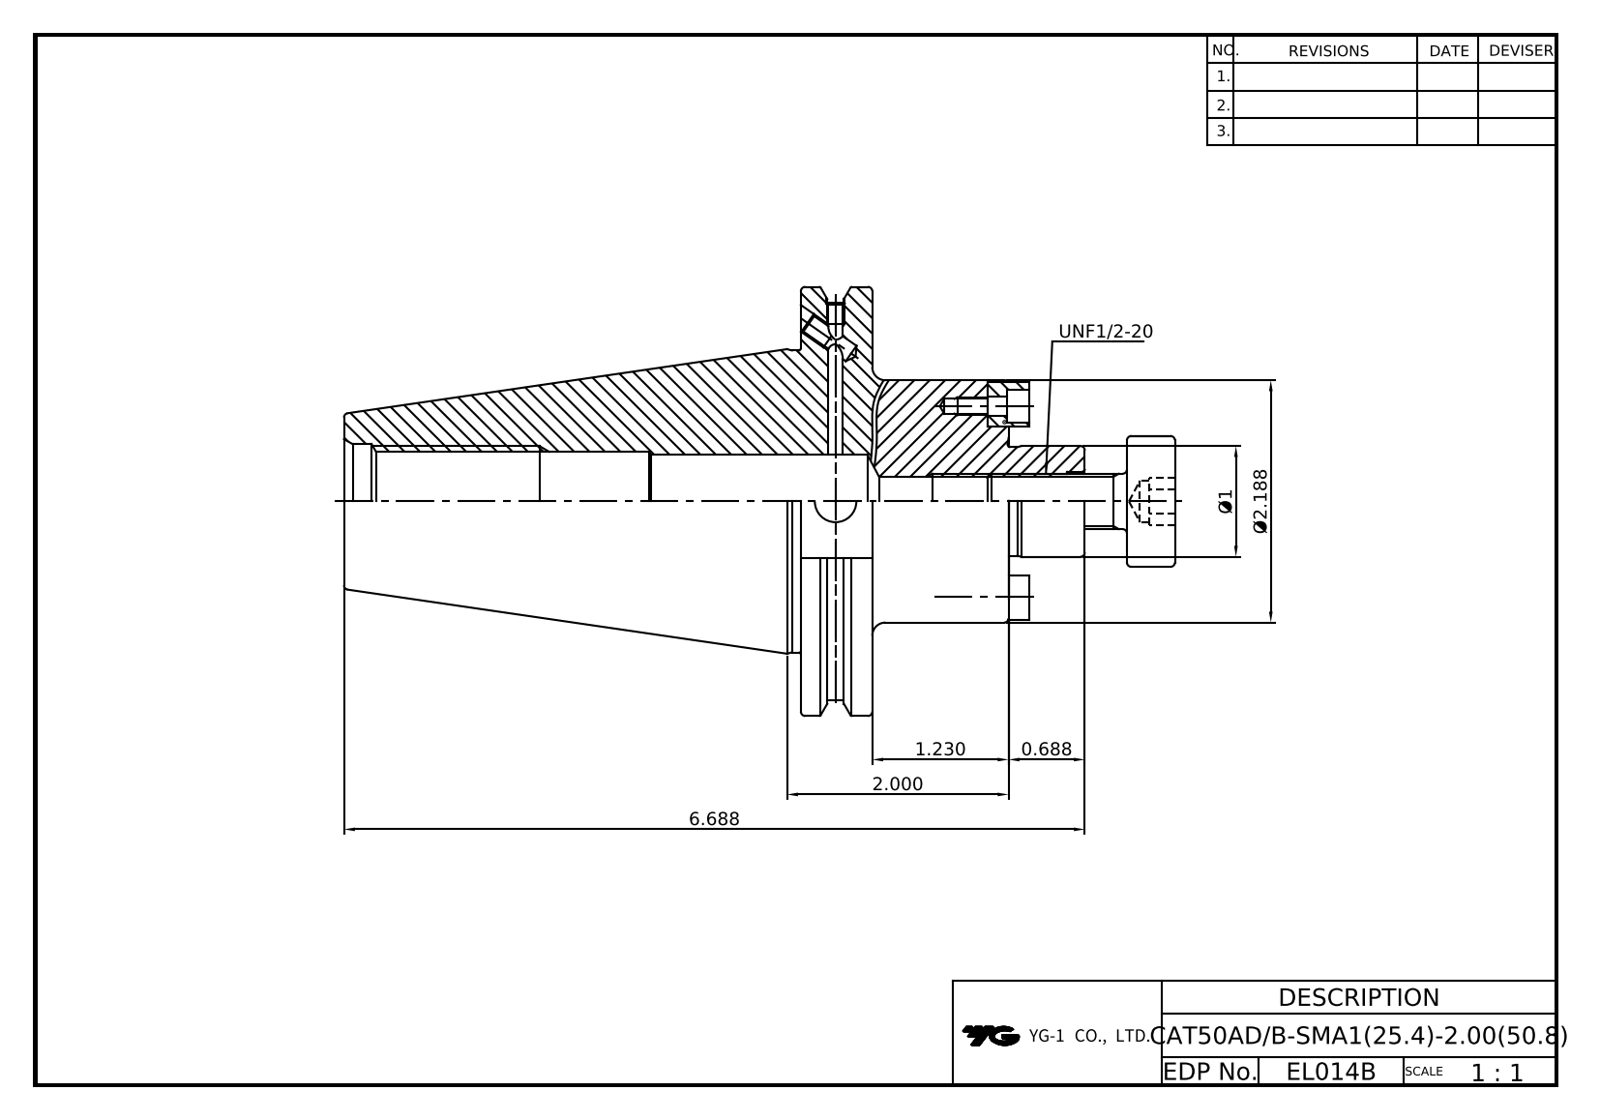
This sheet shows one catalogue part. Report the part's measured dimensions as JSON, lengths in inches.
{"part_name": "LO-CAT50ADB-SMA25.4-50.8; DRIVE KEY-9.52x9.52x10.2; HEX'' WRENCH BOLT-UNC#8-32x3_8L; COLLAR BOLT-UNF1_2-20x32L", "step_written_by": "Autodesk Inventor 2025 (AP242_MANAGED_MODEL_BASED_3D_ENGINEERING_MIM_LF)", "units": "inches", "bodies": {"solids": 6, "faces": 167, "planar": 88, "cylindrical": 43, "other": 36}, "overall_size": [7.515, 3.875, 3.728], "volume_in3": 25.36, "surface_area_in2": 92.3, "round_holes": [[0.128, 2], [0.13, 2], [0.163, 2], [0.165, 2], [0.177, 2], [0.197, 2], [0.295, 2], [0.375, 2], [0.446, 1], [0.531, 1], [0.865, 1], [1.031, 1]], "round_bosses_or_shafts": [[0.27, 2], [0.164, 2], [3.875, 1], [3.594, 1], [2.726, 1], [2.188, 1], [1.181, 1], [1, 1]], "partial_cylinders_radius": [[0.187, 2]], "face_to_face_distances": [0.625, 1.875, 1.25, 2.765, 3.39, 1.515, 4.125, 4.75, 6, 7.515], "hole_center_spacings": [0.86, 1.72]}
